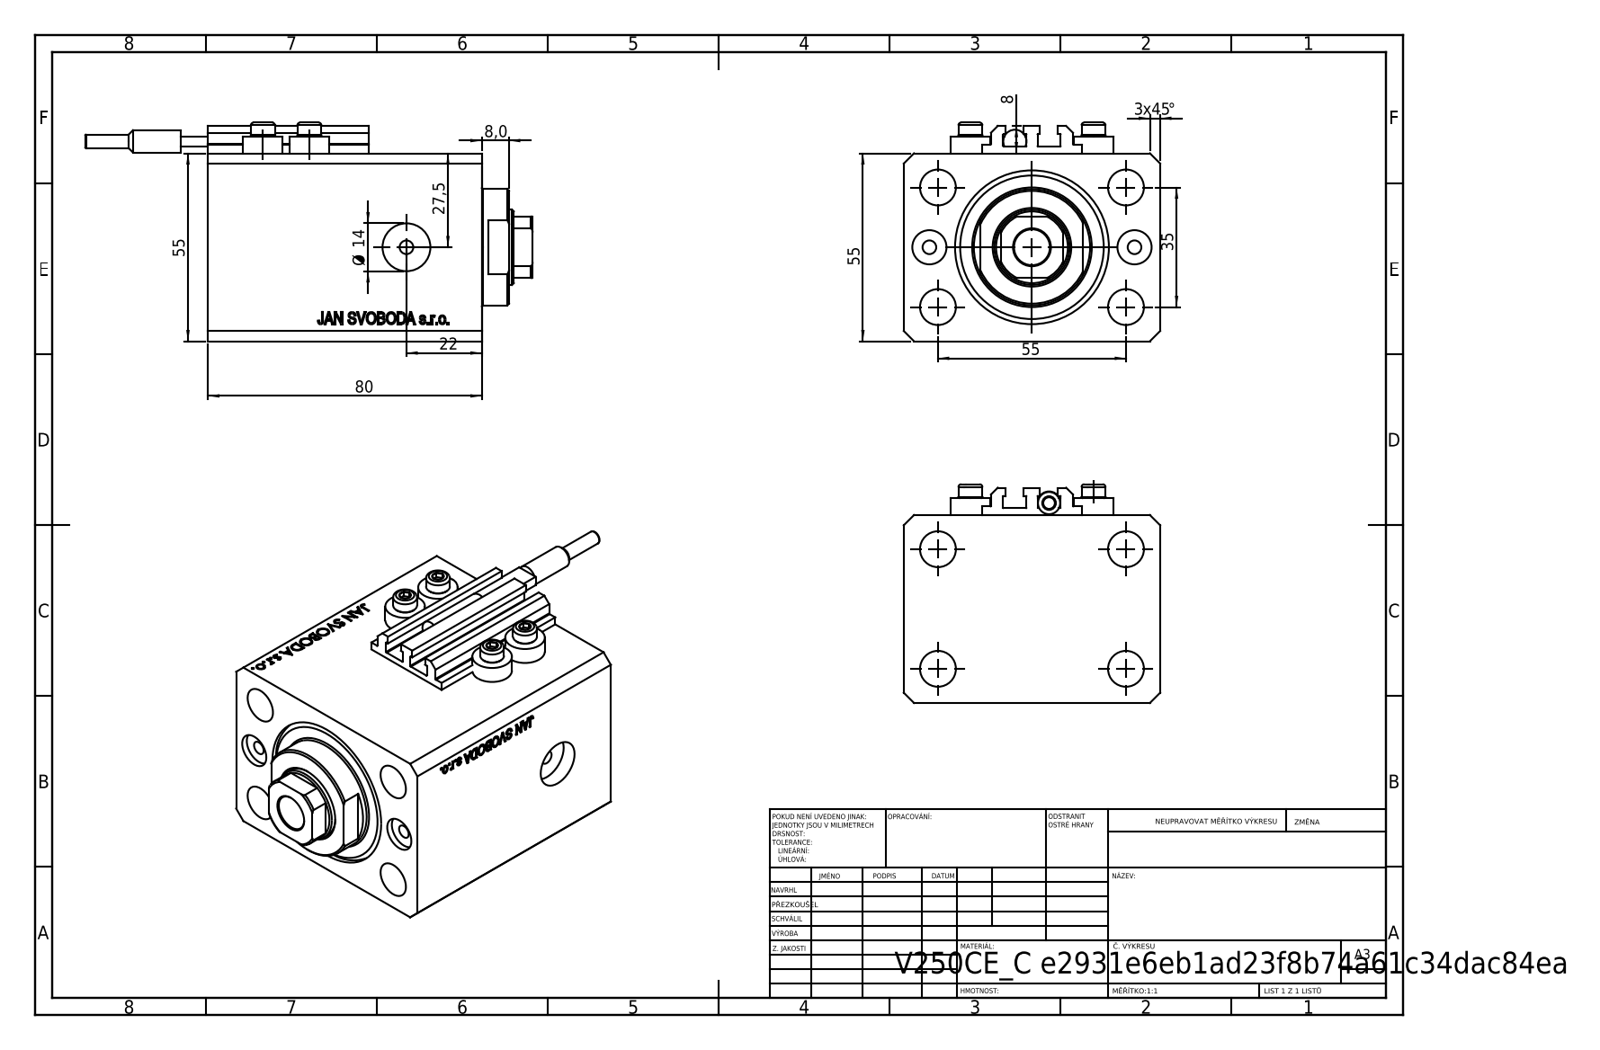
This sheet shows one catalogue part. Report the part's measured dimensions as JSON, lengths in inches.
{"part_name": "V250CE_C; V250CE_C_VCP; SWITCH_V250CE; ALLEN BOLT V250CE (+1 more)", "step_written_by": "SolidWorks 2019 (CONFIG_CONTROL_DESIGN)", "units": "inches", "bodies": {"solids": 9, "faces": 1059, "planar": 519, "cylindrical": 92, "other": 448}, "overall_size": [5.154, 2.953, 2.52], "volume_in3": 18.72, "surface_area_in2": 117, "round_holes": [[0.157, 8], [0.413, 5], [0.394, 2], [0.551, 2], [0.866, 1], [1.26, 1], [1.772, 1]], "round_bosses_or_shafts": [[0.457, 4], [0.276, 4], [1.339, 1], [0.268, 1], [0.256, 1], [0.157, 1]], "partial_cylinders_radius": [[0.008, 10], [0.413, 1]], "face_to_face_distances": [2.165, 2.953, 3.15, 1.067, 2.083, 0.39, 1.693, 2.76, 0.118, 0.315], "hole_center_spacings": [0.696, 1.283, 2.366, 1.417, 0.535, 1.181, 1.378, 1.515]}
